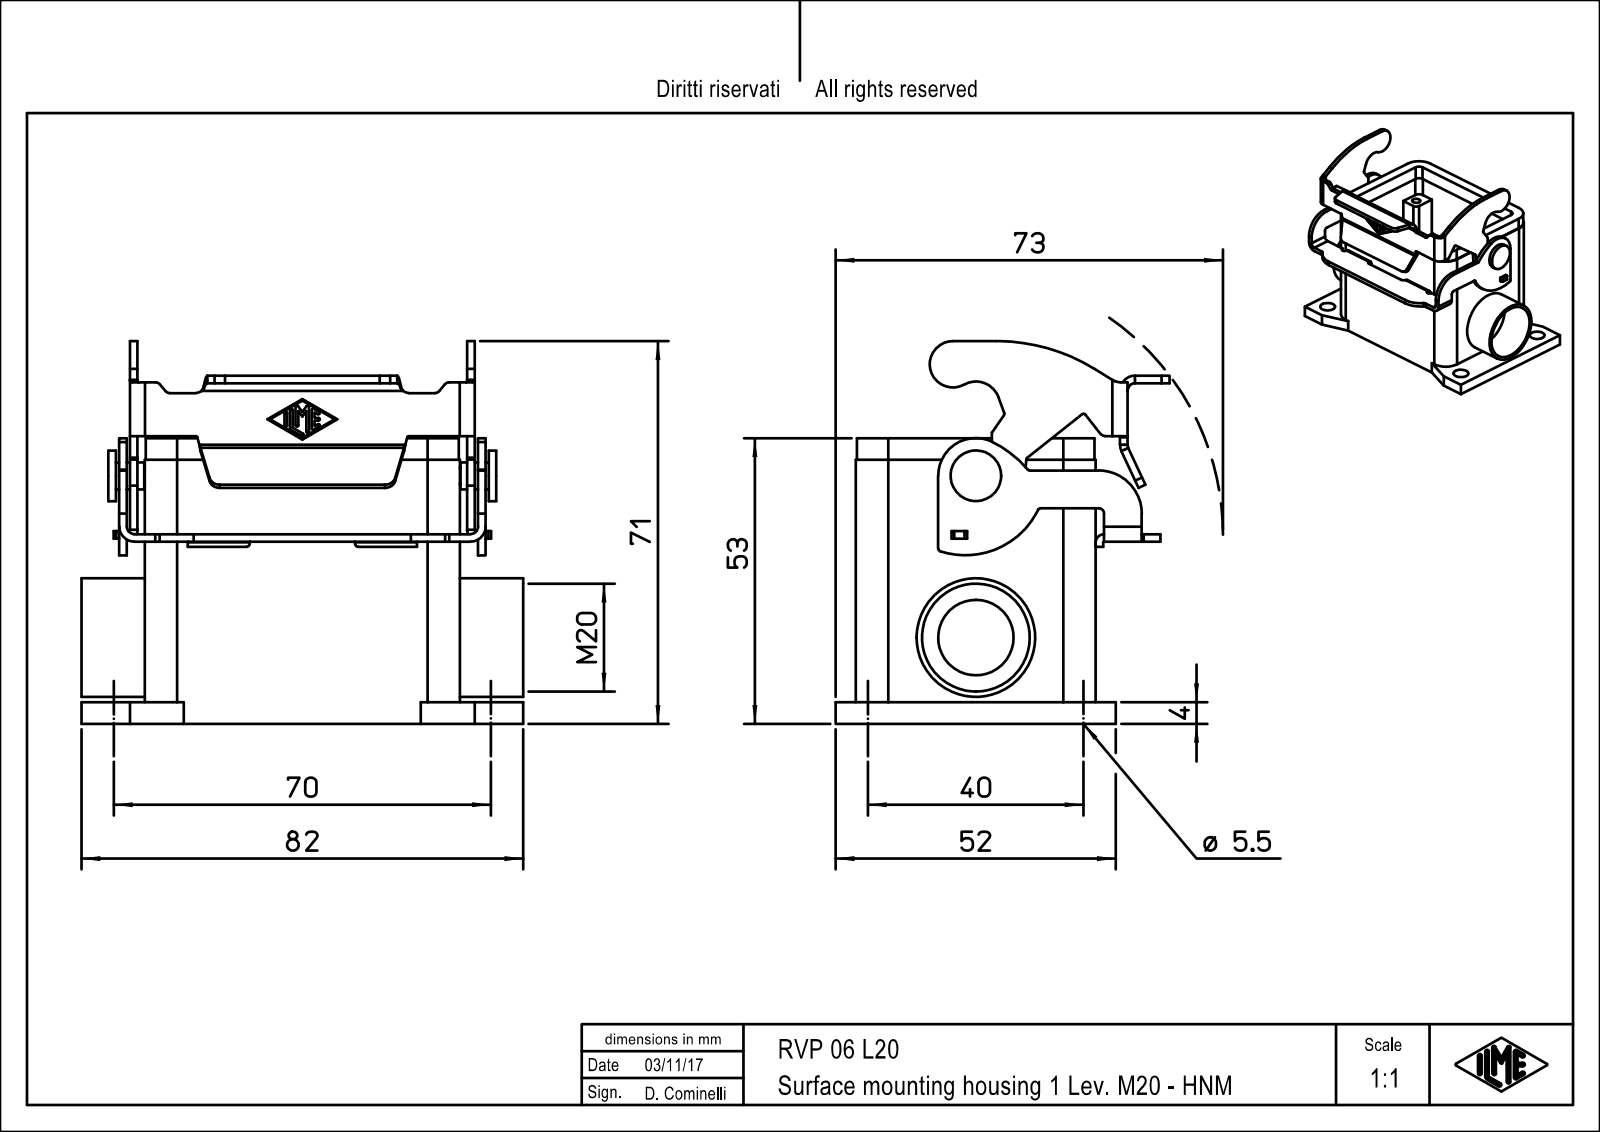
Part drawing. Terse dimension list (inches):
name: RVP_06_L20
written by: PTC Creo Elements/Direct Modeling 19.0E 27-Jun-2016 (C) Parametric Technology GmbH (AUTOMOTIVE_DESIGN)
unit: in
bodies: 1 solid, 381 faces (199 planar, 170 cylindrical, 12 other)
size: 3.228 × 2.795 × 2.44
volume: 4.247 in³; area: 61.67 in²
holes: 4× ⌀0.097, 4× ⌀0.118, 4× ⌀0.217, 1× ⌀0.551, 1× ⌀0.787
bosses: 1× ⌀0.866, 1× ⌀0.37, 1× ⌀0.197, 1× ⌀0.118
rounds: 16× R0.01, 12× R0.02, 12× R0.039, 11× R0.059, 8× R0.079, 6× R0.055, 6× R0.11, 4× R0.071
face distances: 0.157, 0.055, 1.594, 1.752, 0.079, 2.543, 0.266, 1.437, 1.988, 0.423
hole spacings: 0.572, 1.415, 2.259, 2.603, 1.063, 1.575, 1.732, 2.032
